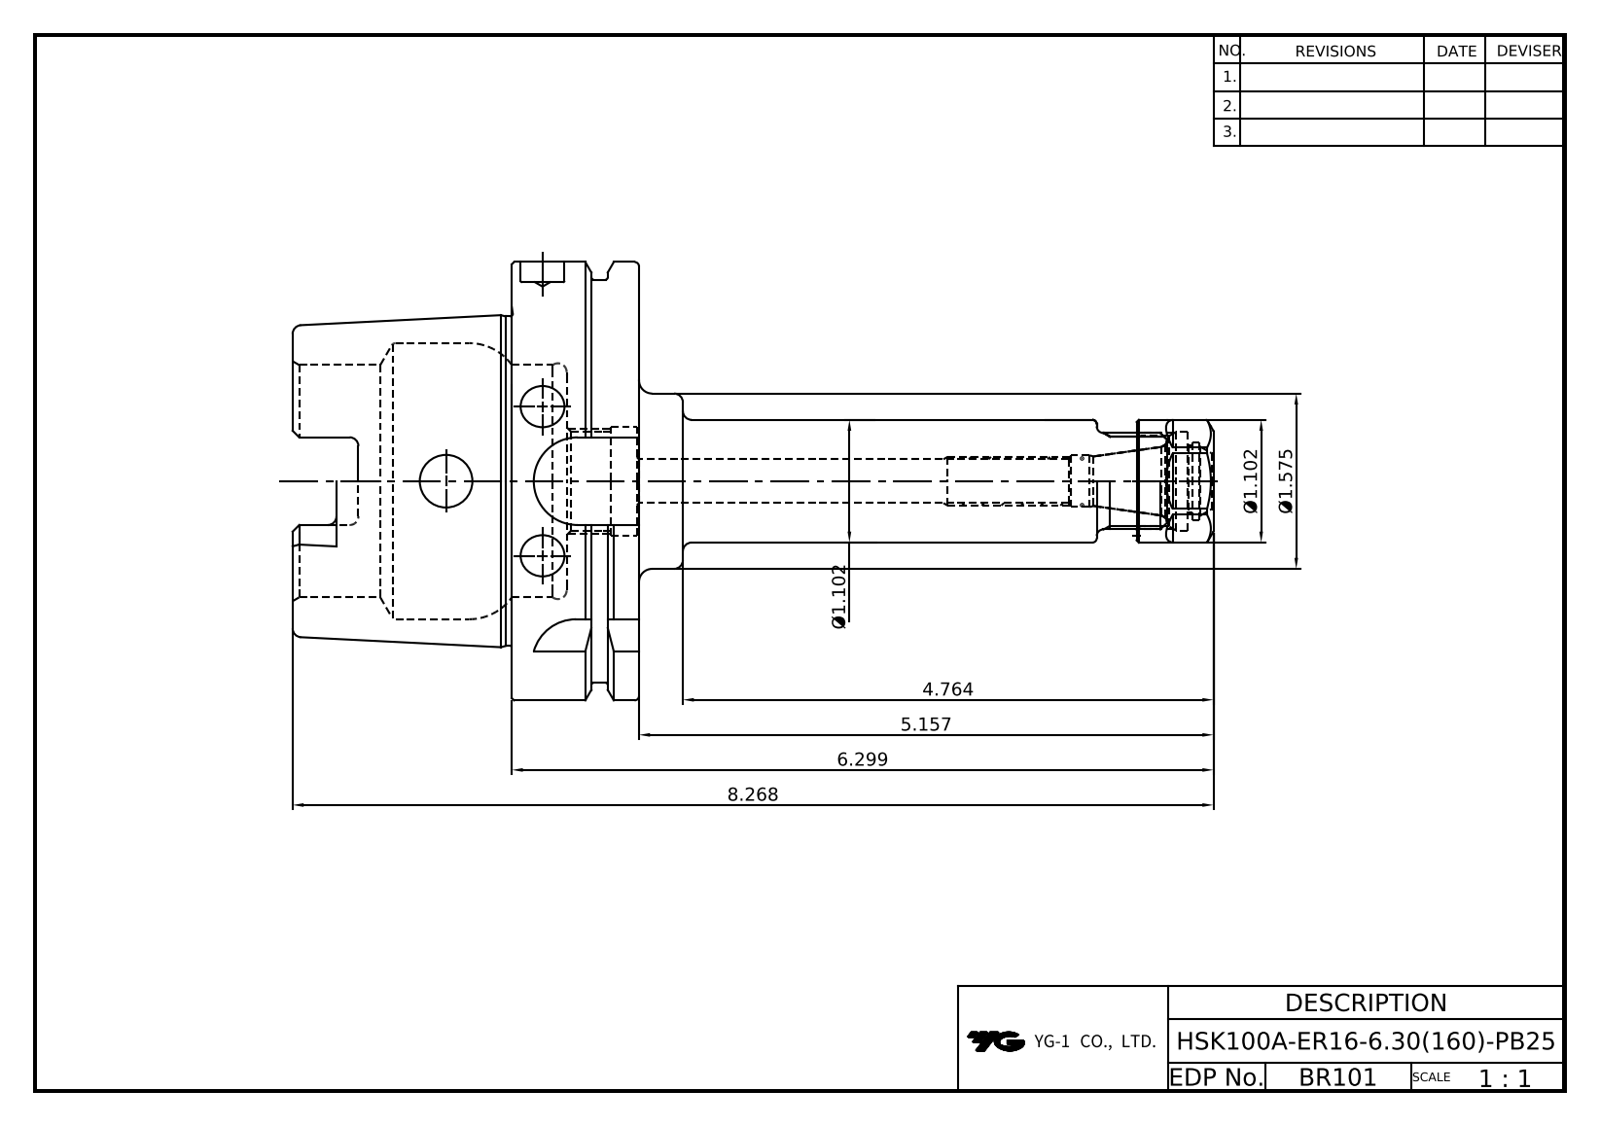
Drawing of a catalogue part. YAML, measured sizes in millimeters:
part_name: "LO-HSK100A-ER16-6.30; ER16NUT"
step_written_by: "Autodesk Inventor 2025 (AUTOMOTIVE_DESIGN)"
units: millimeters
bodies: {solids: 2, faces: 154, planar: 58, cylindrical: 44, other: 52}
overall_size: [210, 100, 100]
volume: 326164
surface_area: 67602
round_holes:
  - {diameter: 1, count: 1}
  - {diameter: 9.4, count: 1}
  - {diameter: 10, count: 1}
  - {diameter: 11.8, count: 1}
  - {diameter: 12, count: 1}
  - {diameter: 12.8, count: 1}
  - {diameter: 17.7, count: 1}
  - {diameter: 20.6, count: 1}
  - {diameter: 22.38, count: 1}
  - {diameter: 22.5, count: 1}
  - {diameter: 25, count: 1}
  - {diameter: 53, count: 1}
round_bosses_or_shafts:
  - {diameter: 100, count: 1}
  - {diameter: 92, count: 1}
  - {diameter: 75.41, count: 1}
  - {diameter: 40, count: 1}
  - {diameter: 28, count: 1}
  - {diameter: 22, count: 1}
partial_cylinders:
  - {radius: 2, count: 6}
  - {radius: 4.88, count: 4}
  - {radius: 10, count: 4}
  - {radius: 7.7, count: 2}
face_to_face_distances: [29, 12.5, 16.5, 79, 62.5, 50, 10, 16, 88, 78.5]
hole_center_spacings: [12]
